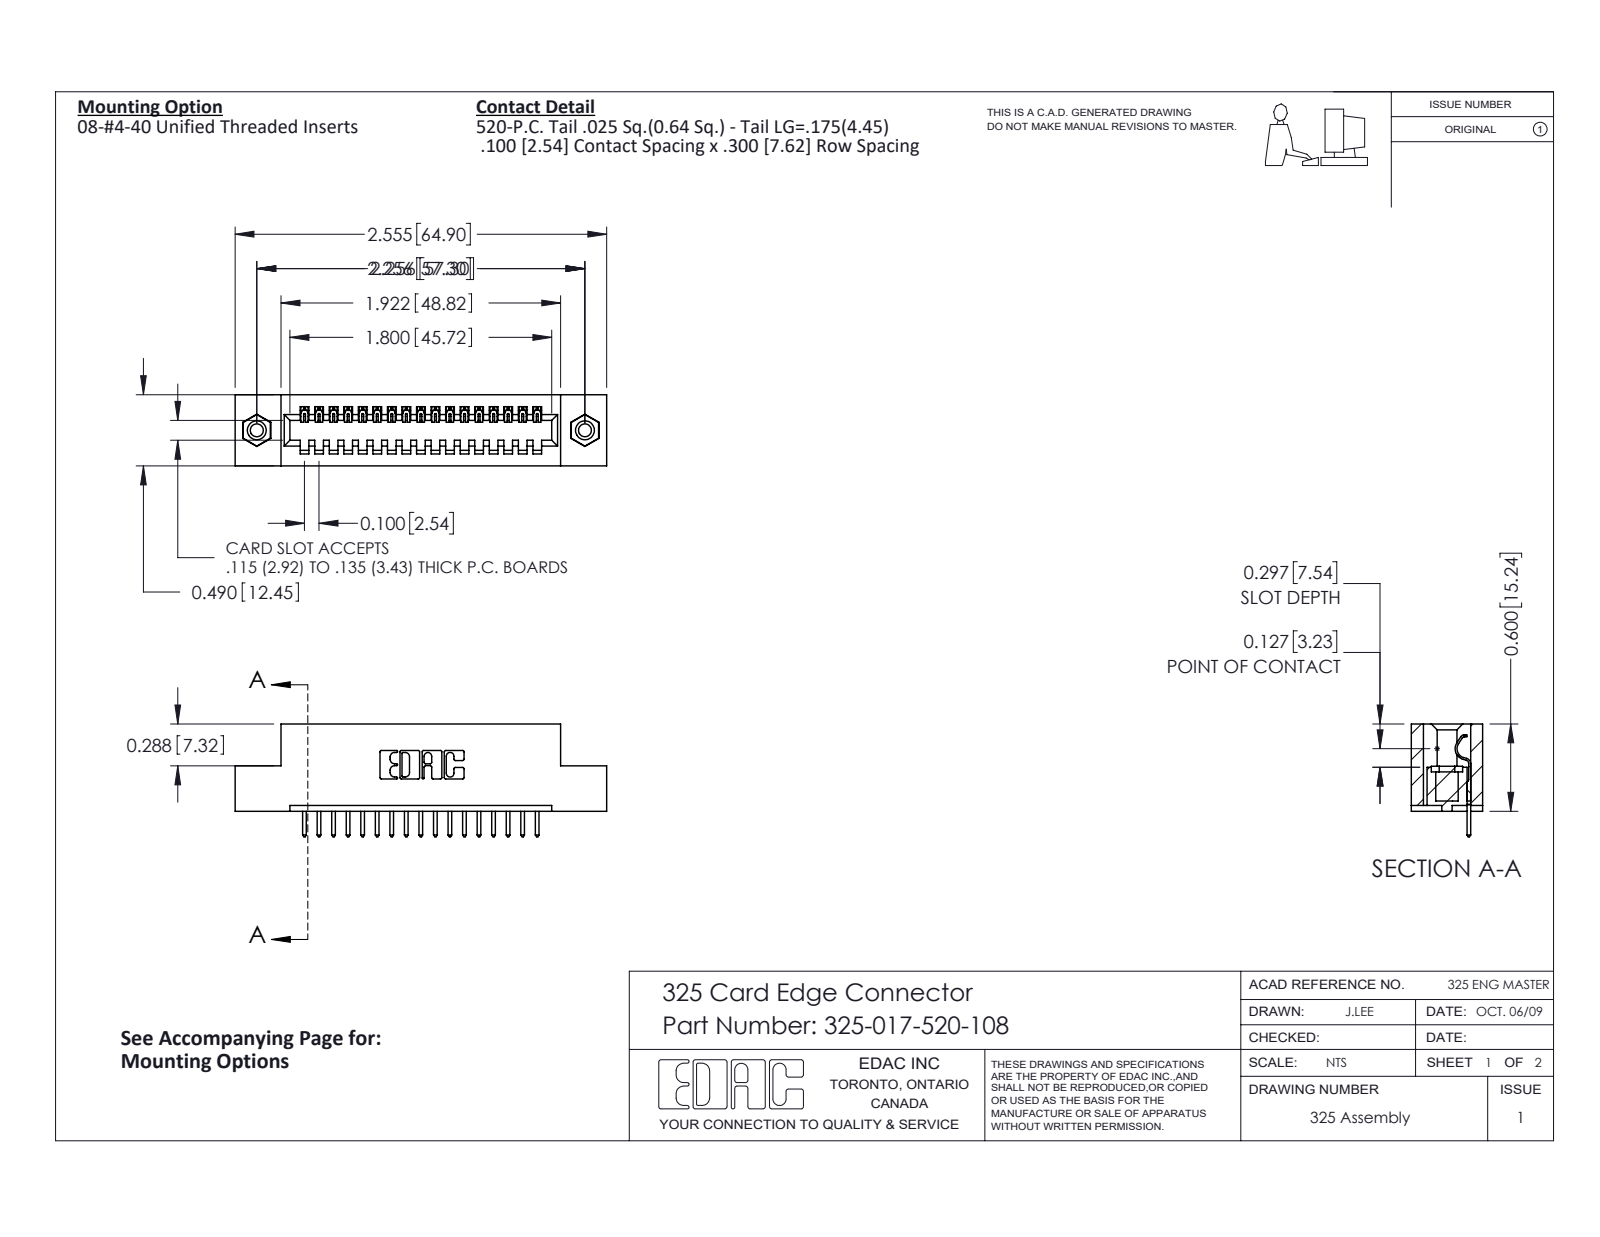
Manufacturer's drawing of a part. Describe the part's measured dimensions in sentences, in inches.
The part is named "345-250-001_345-250-003-102; 325-292-001_325-293-120; 325-017-520-108; 325 Part_TI". Its 3-D file was written by "SolidWorks 2016 (CONFIG_CONTROL_DESIGN)". It is 20 solids with 1160 faces: 816 planar, 328 cylindrical and 16 other. Overall it measures 2.555 by 0.775 by 0.49 inches. Its volume is 0.488 cubic inches and its surface area 12.62 square inches. Round holes: 2 of diameter 0.089, 2 of diameter 0.125, 2 of diameter 0.16. Round bosses or shafts: 2 of diameter 0.155. Partial cylindrical surfaces (rounded edges, fillets, slot ends): 34 of radius 0.006, 34 of radius 0.01, 22 of radius 0.01, 6 of radius 0.007, 6 of radius 0.031, 3 of radius 0.026, 1 of radius 0.014, 1 of radius 0.022. The main face-to-face distances are 0.083, 0.407, 0.3, 0.49, 0.6, 0.107, 0.383, 0.025, 0.04, 0.2. The hole center spacings are 2.256.
